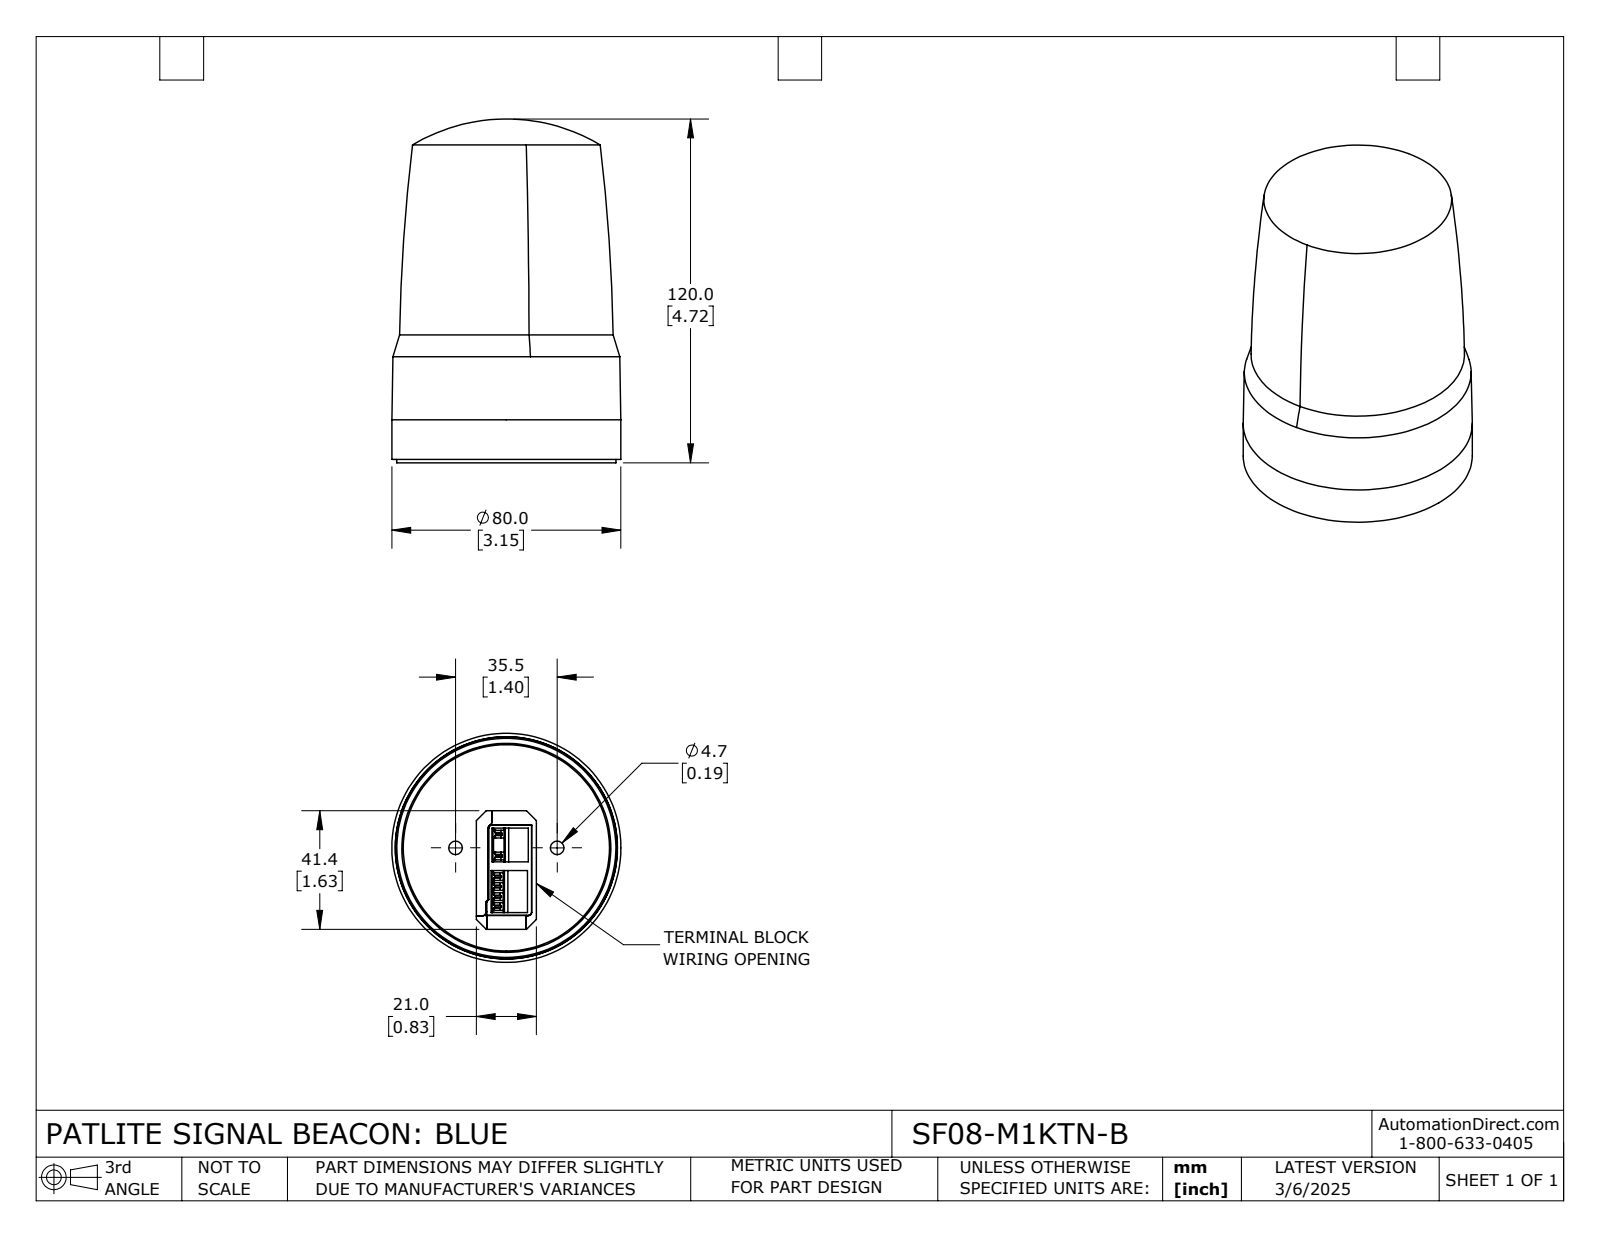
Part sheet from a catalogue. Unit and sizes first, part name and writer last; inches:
Units: inches
Overall size (bounding box): 4.724 × 3.15 × 3.15
Round holes (diameter × count): ⌀0.185 ×2, ⌀0.48 ×2, ⌀2.874 ×1
Round bosses / shafts (diameter × count): ⌀3.15 ×1, ⌀3.012 ×1, ⌀2.937 ×1, ⌀2.835 ×1
Partial cylindrical surfaces — rounded edges, fillets, slot ends (radius × count): R1.319 ×1, R1.362 ×1
Main face-to-face distances: 0.248, 0.185, 0.433, 0.071, 0.504, 0.256, 0.059, 0.374, 0.126, 0.13
Hole centre spacings: 0.699, 1.398
Volume: 29.01 in³ · Surface area: 81.21 in²
Bodies: 2 solids, 287 faces (199 planar, 23 cylindrical, 65 other)
Part name (STEP PRODUCT): SF08-M1KTN-B
STEP written by: SolidWorks 2024 (CONFIG_CONTROL_DESIGN)
